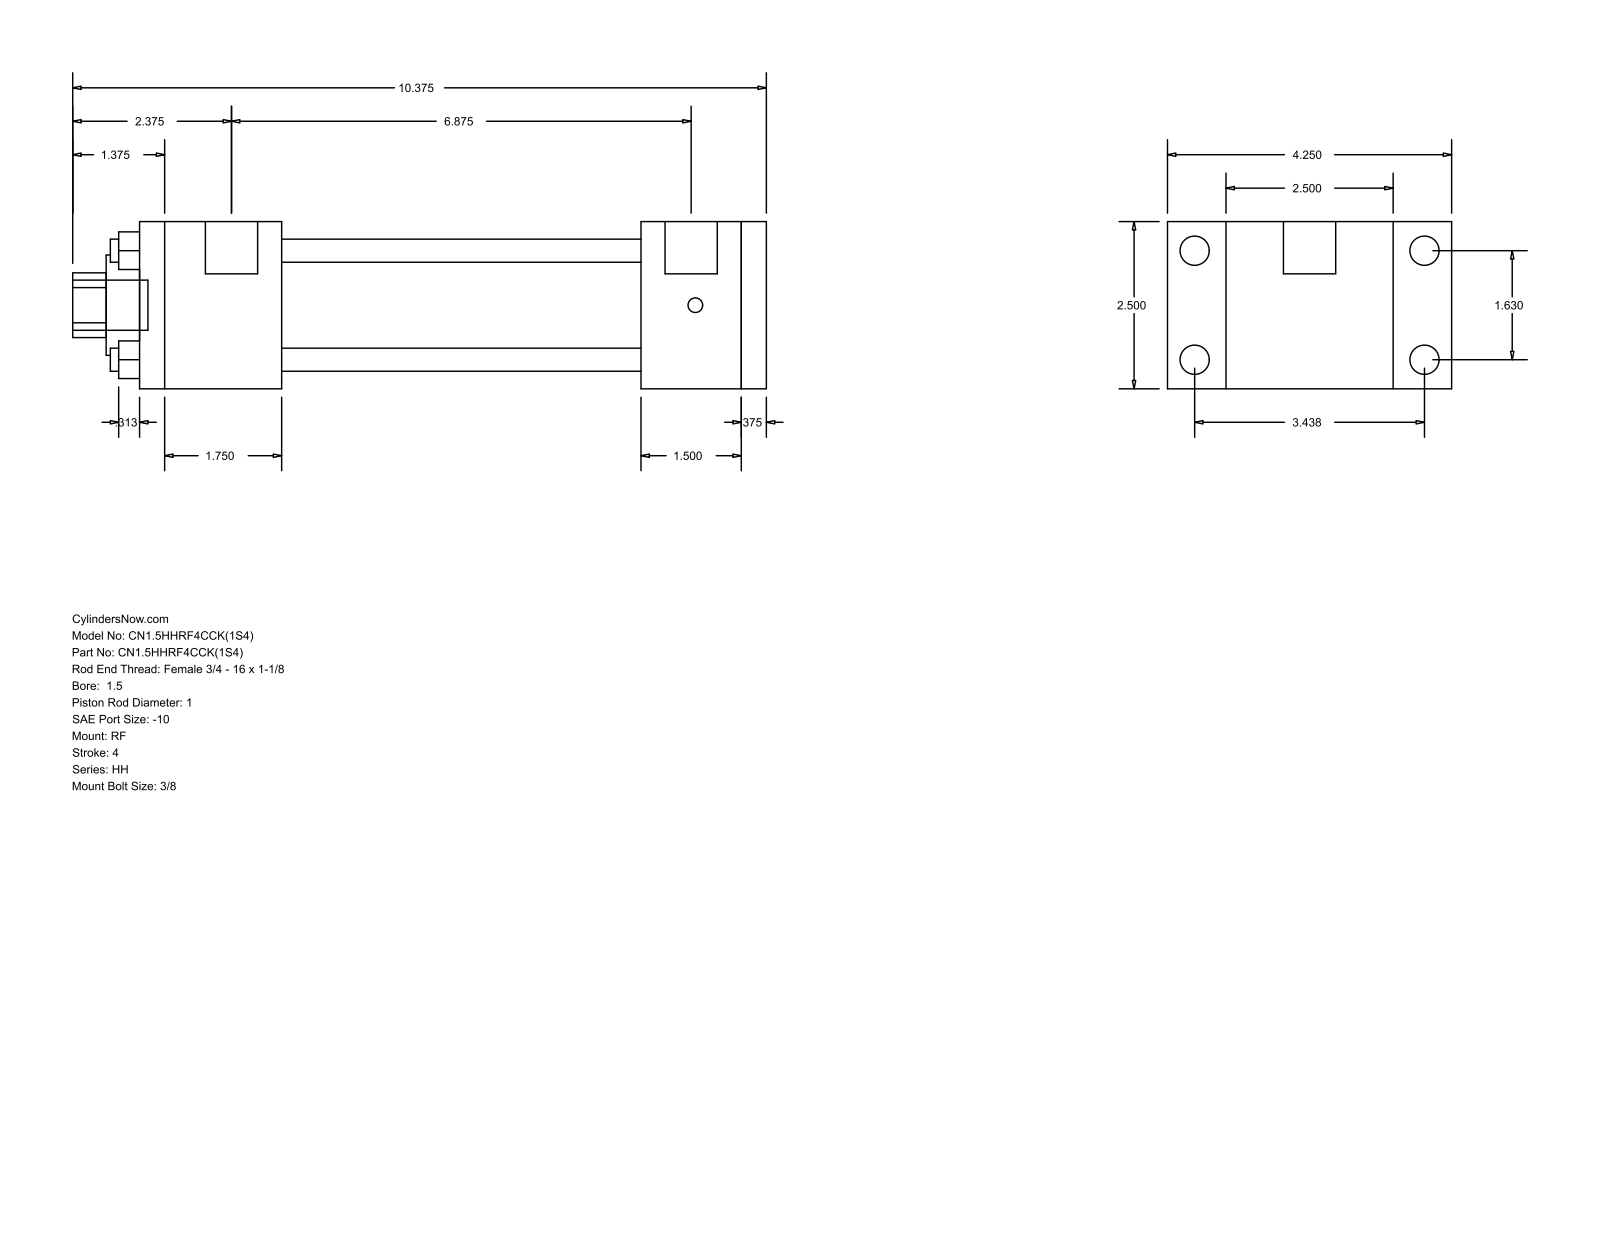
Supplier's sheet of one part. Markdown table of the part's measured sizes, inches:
| quantity | value |
| --- | --- |
| part name | HH_RF__0150_1 |
| STEP written by | GSSL Pune (CONFIG_CONTROL_DESIGN) |
| units | inches |
| bodies | 0 solids, 92 faces (64 planar, 28 cylindrical, 0 other) |
| overall size | 10.375 × 4.25 × 2.5 |
| round holes (diameter × count) | 0.345 × 4, 1 × 1, 1.5 × 1, 1.75 × 1 |
| round bosses / shafts (diameter × count) | 0.438 × 4, 0.219 × 4, 0.781 × 2, 0.75 × 1 |
| partial cylindrical surfaces (radius × count) | 0.484 × 1 |
| main face-to-face distances | 2.5, 0.375, 5.375, 6.875, 7.25, 1.5, 1.875, 2.125, 7.5, 9 |
| hole center spacings | 1.152, 1.63, 2.305 |
